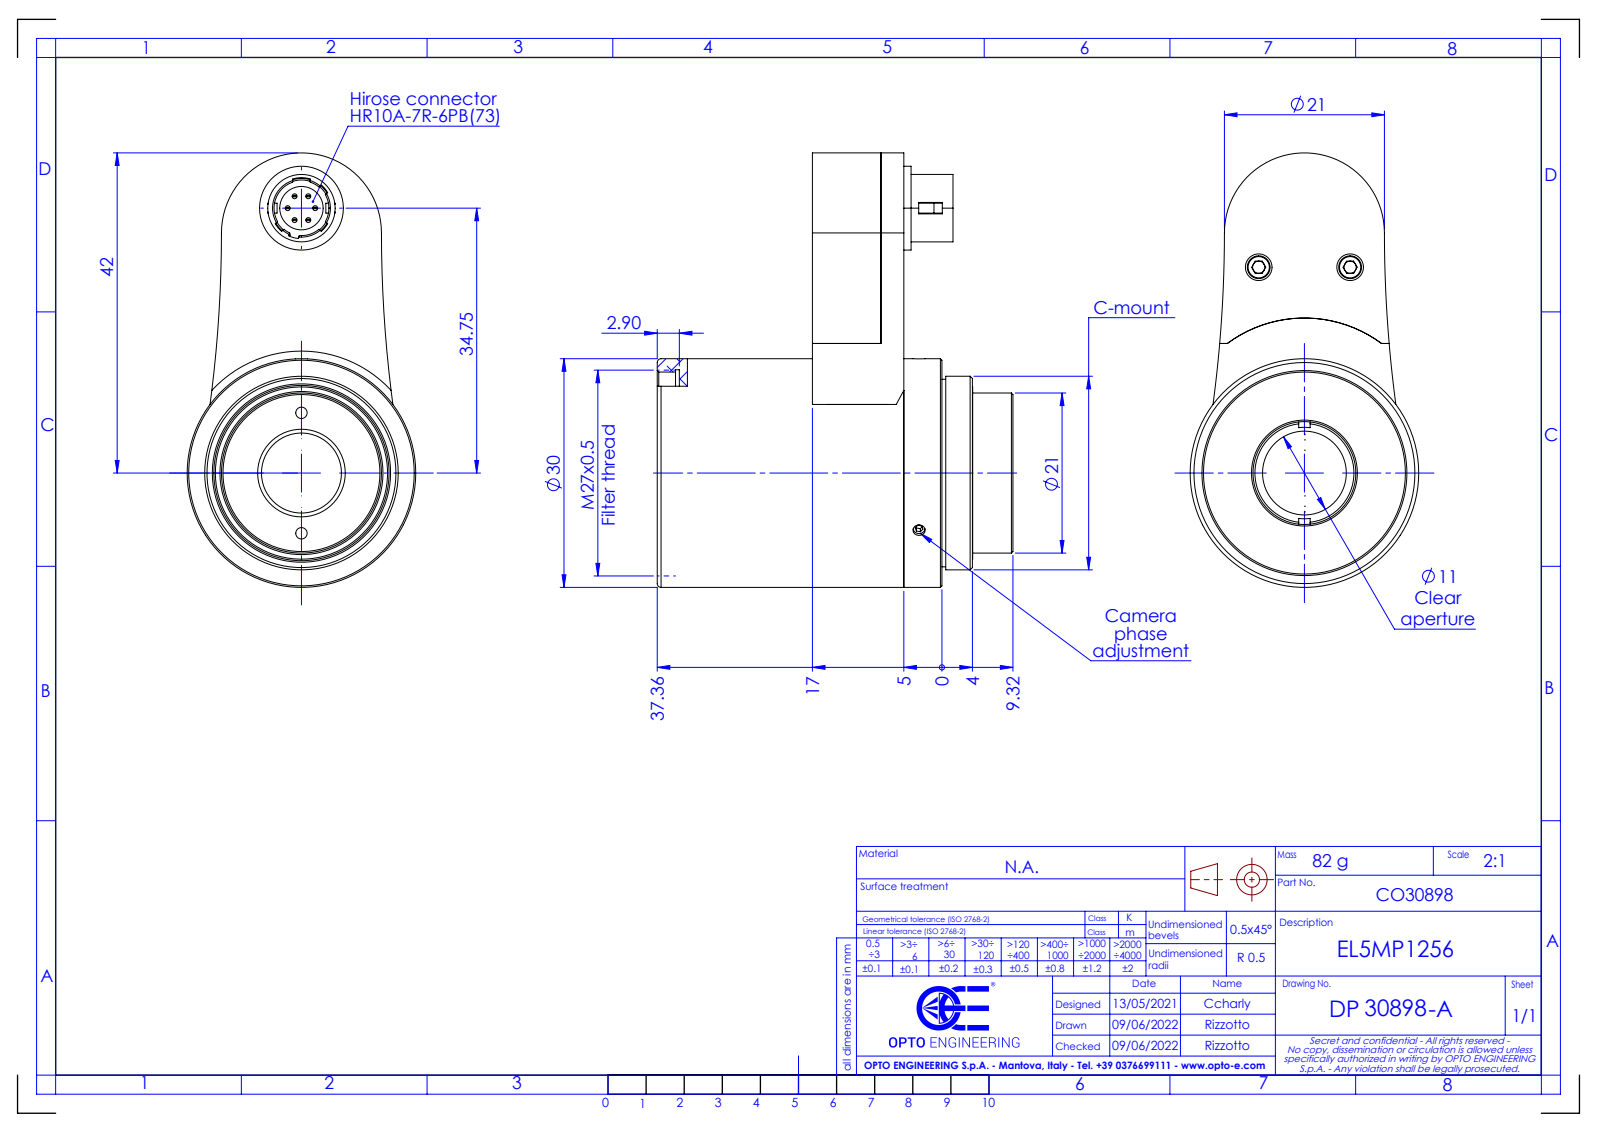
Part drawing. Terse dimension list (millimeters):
name: DP30898-A_EL5MP1256
written by: SolidWorks 2021 (CONFIG_CONTROL_DESIGN)
unit: mm
bodies: 0 solids, 219 faces (91 planar, 86 cylindrical, 42 other)
size: 57 × 46.69 × 30
holes: 3× ⌀1.6, 2× ⌀1.5, 2× ⌀3.5, 1× ⌀7.4, 1× ⌀10.5, 1× ⌀11, 1× ⌀13.5, 1× ⌀23, 1× ⌀26.5, 1× ⌀27.1
bosses: 2× ⌀3, 2× ⌀1.2, 1× ⌀30, 1× ⌀25.4, 1× ⌀24.6, 1× ⌀21, 1× ⌀11, 1× ⌀8.85
rounds: 2× R0.4, 2× R169.5, 1× R3.6, 1× R3.9, 1× R4, 1× R10.5, 1× R17
face distances: 12, 17.46, 29.46, 43.78, 26.32, 14.32, 34.46, 17, 5, 9.32
hole spacings: 7.9, 9.8, 20.02, 27.66, 35.41, 12, 15.8, 26.85
